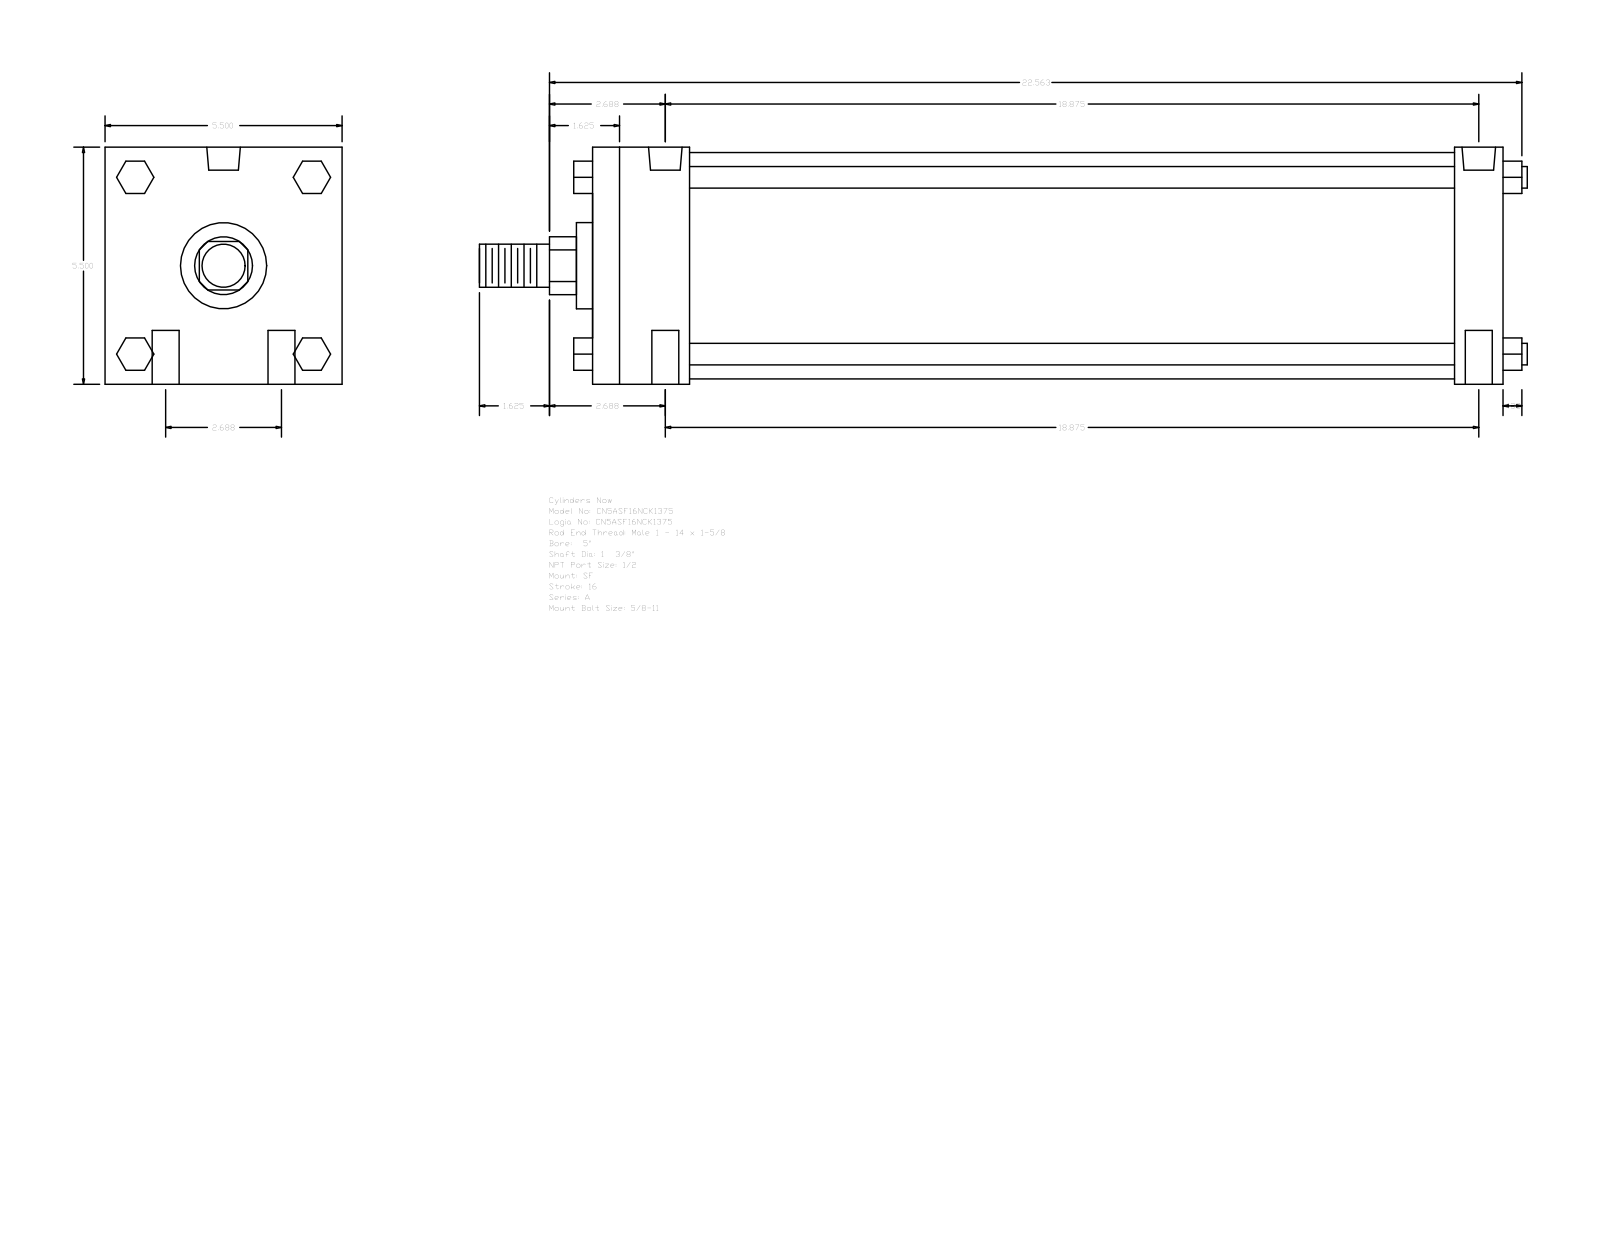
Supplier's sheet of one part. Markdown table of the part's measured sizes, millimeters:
| quantity | value |
| --- | --- |
| part name | A_SF__0500_1.375 |
| STEP written by | GSSL Pune (CONFIG_CONTROL_DESIGN) |
| units | millimeters |
| bodies | 0 solids, 124 faces (94 planar, 30 cylindrical, 0 other) |
| overall size | 617.54 × 139.7 × 139.7 |
| round holes (diameter × count) | 15.88 × 4, 8.73 × 2, 19.77 × 2 |
| round bosses / shafts (diameter × count) | 12.7 × 4, 133.35 × 1, 50.8 × 1, 34.92 × 1, 25.4 × 1 |
| partial cylindrical surfaces (radius × count) | 17.06 × 1 |
| main face-to-face distances | 139.7, 536.58, 57.15, 28.58, 508, 450.85, 479.43, 19.05, 52.07, 90.18 |
| hole center spacings | 34.13, 480.64, 479.43, 68.26, 484.26, 474.65 |
